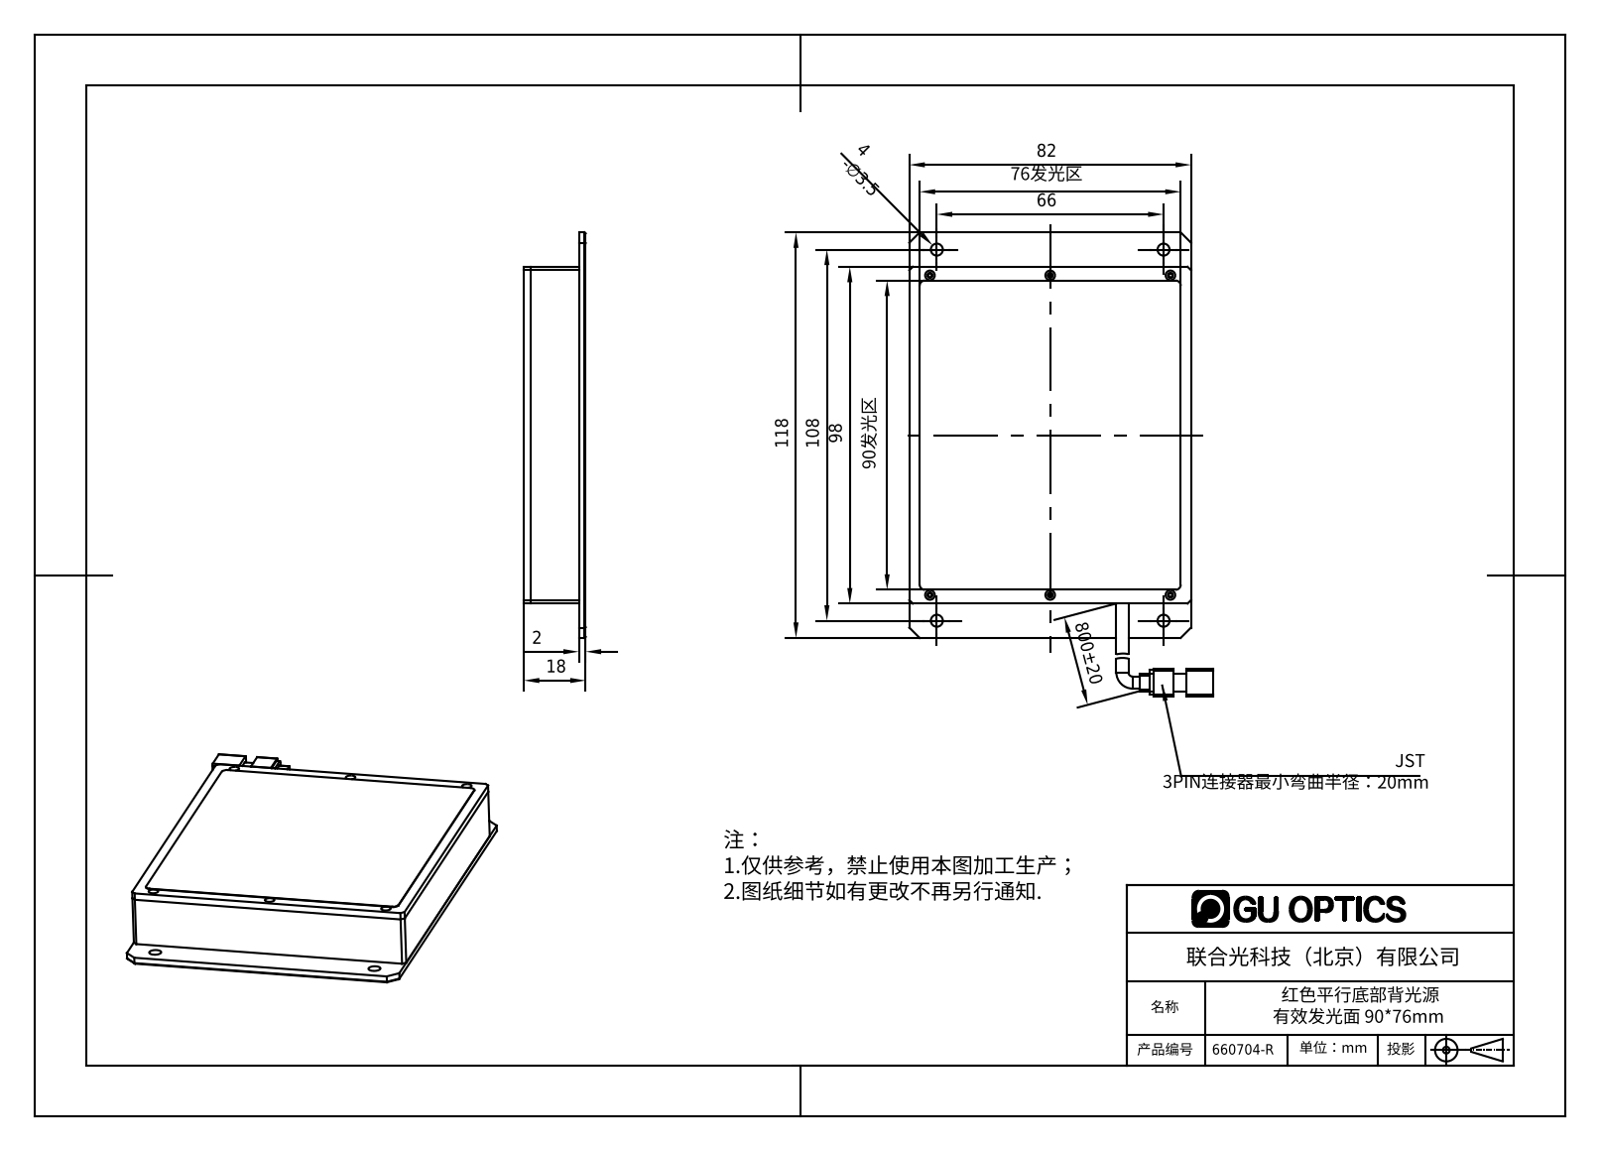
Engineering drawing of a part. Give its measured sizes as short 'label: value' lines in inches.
name: 660704-R
written by: SolidWorks 2016 (AUTOMOTIVE_DESIGN)
unit: in
bodies: 6 solids, 1243 faces (1028 planar, 118 cylindrical, 97 other)
size: 5.315 × 3.484 × 0.732
volume: 3.772 in³; area: 104.3 in²
holes: 6× ⌀0.043, 6× ⌀0.049, 6× ⌀0.059, 6× ⌀0.063, 6× ⌀0.087, 6× ⌀0.11, 4× ⌀0.138
bosses: 2× ⌀0.138
rounds: 8× R0.02, 8× R0.039, 4× R0.059, 2× R0.079
face distances: 0.079, 0.63, 0.551, 0.091, 0.539, 0.039, 0.622, 0.634, 0.713, 0.083
hole spacings: 1.378, 1.378, 3.949, 0.039, 3.701, 4.614, 4.777, 0.268
